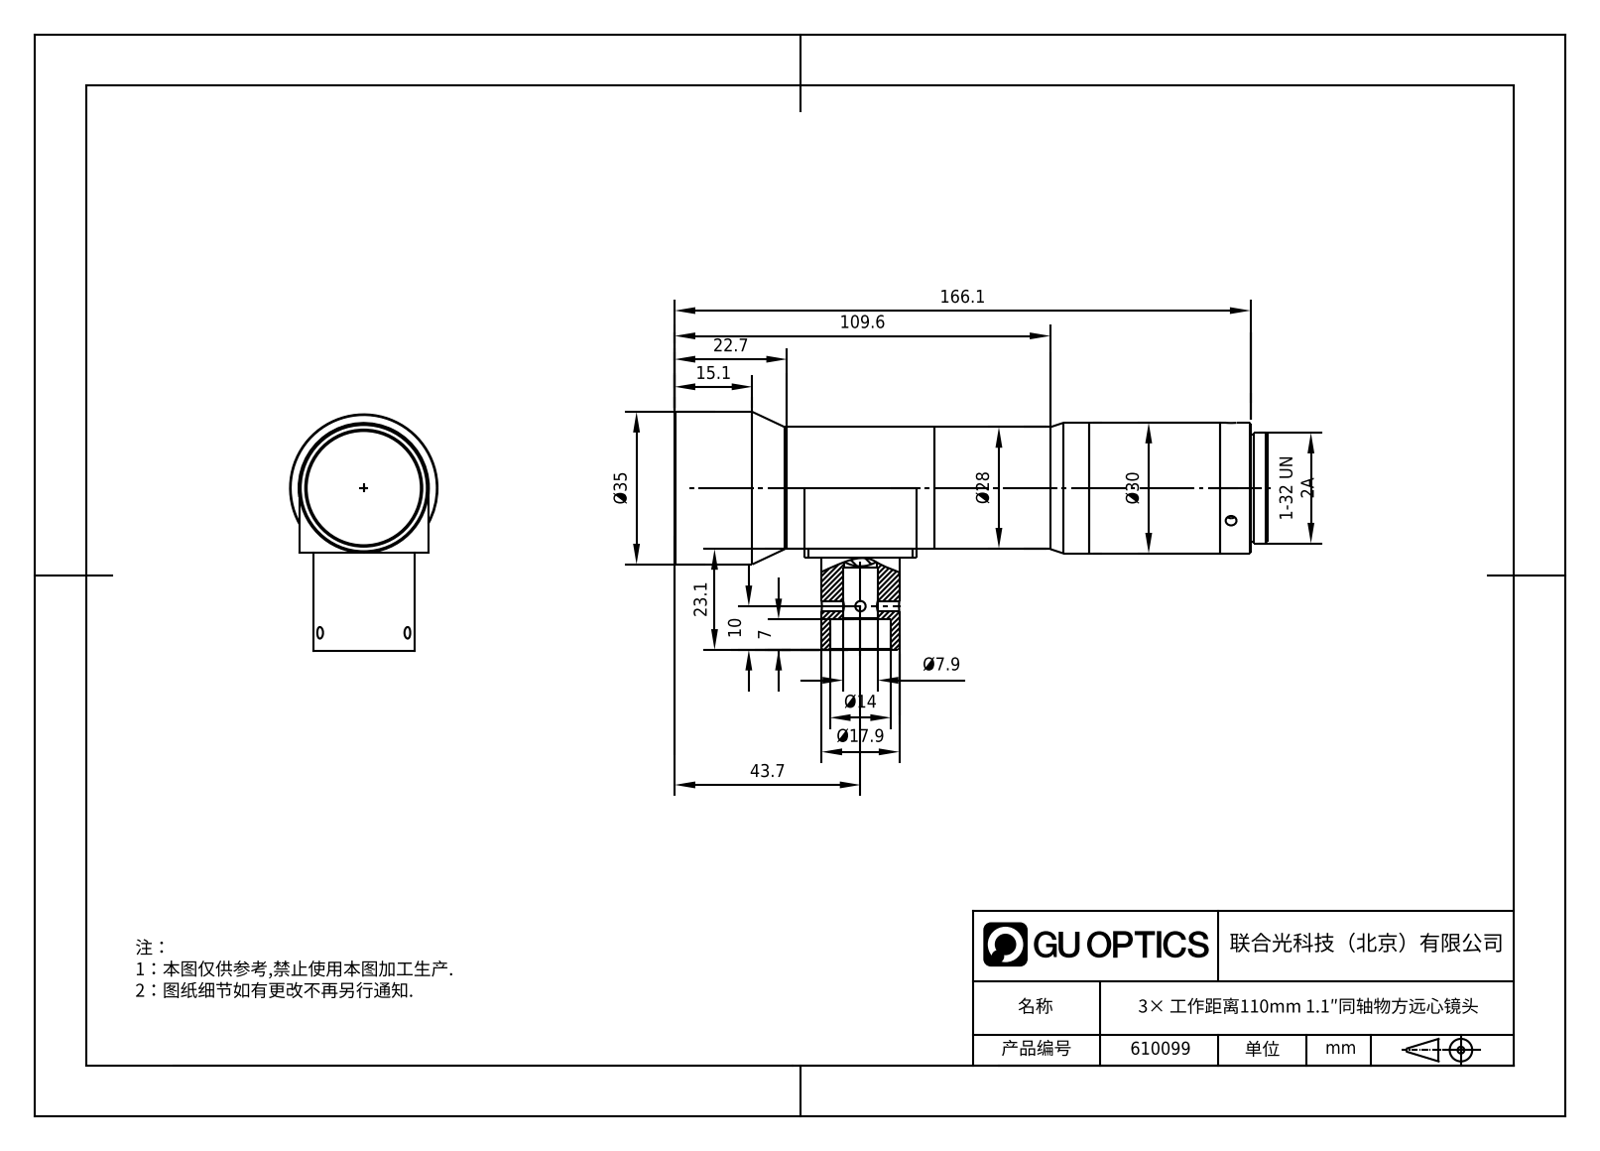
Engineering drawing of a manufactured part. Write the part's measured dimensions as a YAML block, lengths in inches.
part_name: "WWK30-110C-111"
step_written_by: "SolidWorks 2012 (CONFIG_CONTROL_DESIGN)"
units: inches
bodies: {solids: 1, faces: 127, planar: 28, cylindrical: 63, other: 36}
overall_size: [6.691, 2.15, 1.378]
volume: 7.409
surface_area: 32.15
round_holes:
  - {diameter: 0.063, count: 4}
  - {diameter: 0.087, count: 4}
  - {diameter: 0.098, count: 3}
  - {diameter: 0.094, count: 2}
  - {diameter: 0.295, count: 1}
  - {diameter: 0.315, count: 1}
  - {diameter: 0.555, count: 1}
  - {diameter: 0.768, count: 1}
  - {diameter: 0.906, count: 1}
  - {diameter: 1.24, count: 1}
round_bosses_or_shafts:
  - {diameter: 1.378, count: 1}
  - {diameter: 1.181, count: 1}
  - {diameter: 1.102, count: 1}
  - {diameter: 1, count: 1}
  - {diameter: 0.969, count: 1}
  - {diameter: 0.709, count: 1}
partial_cylinders:
  - {radius: 0.242, count: 1}
  - {radius: 0.529, count: 1}
face_to_face_distances: [1.102, 0.154, 6.691, 6.538, 5.485, 5.331, 1.207, 4.461, 4.307, 1.024]
hole_center_spacings: [0.613, 0.827, 0.906, 1.226, 4.253, 5.076, 1.067, 4.642]
